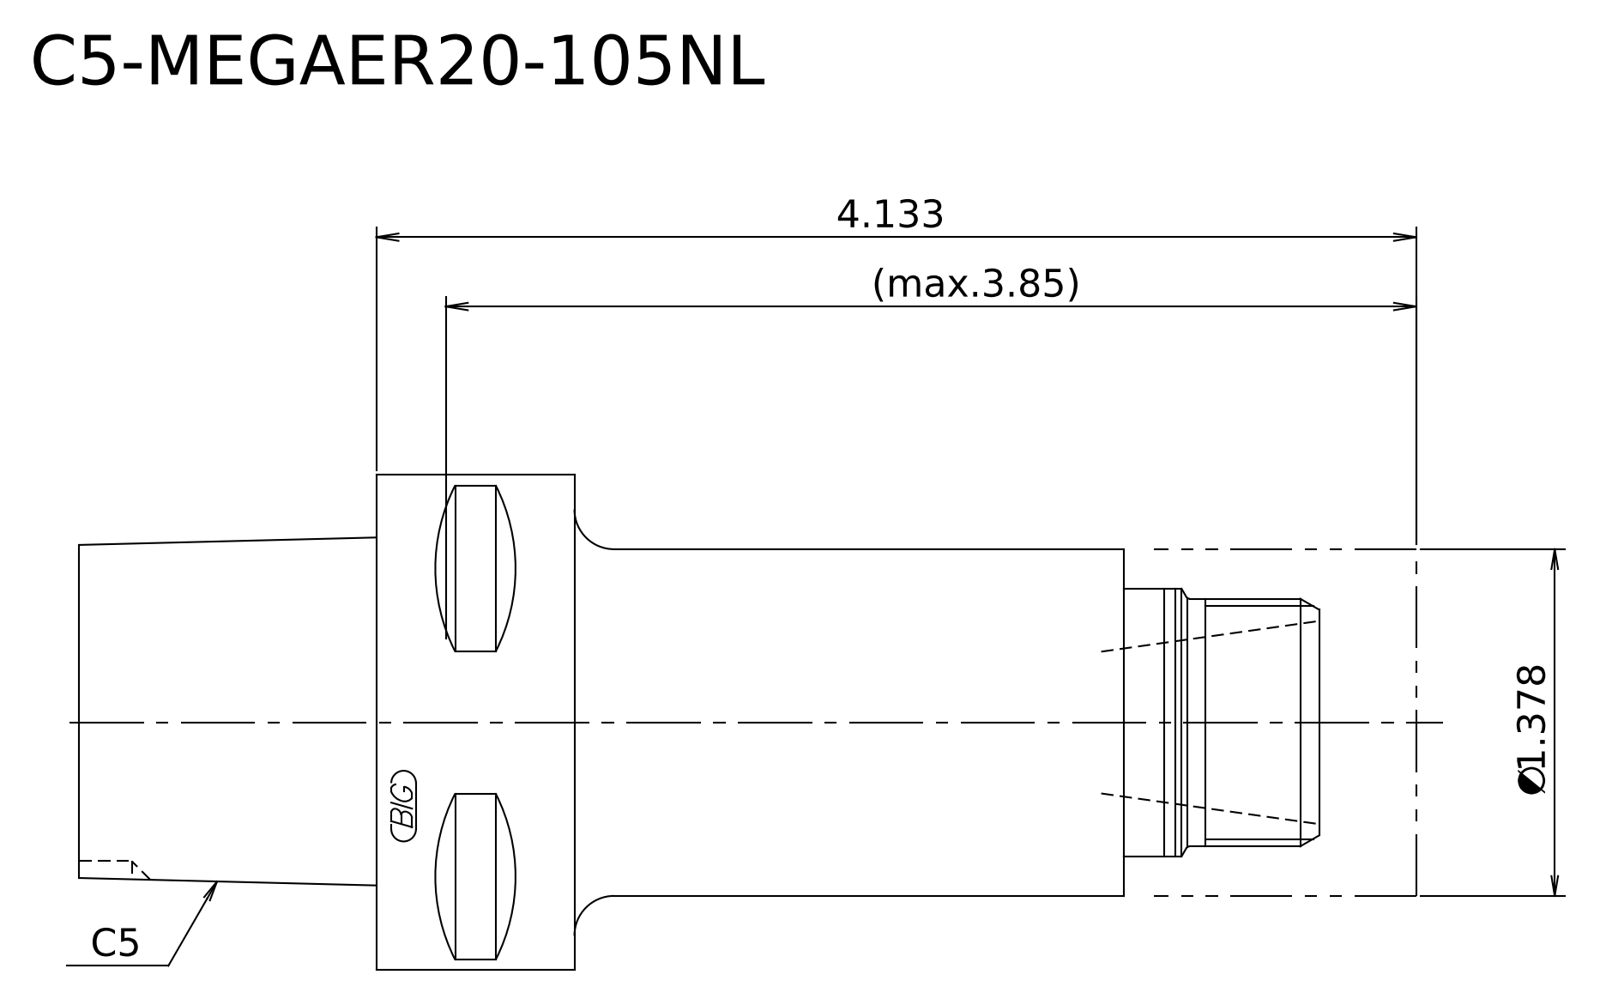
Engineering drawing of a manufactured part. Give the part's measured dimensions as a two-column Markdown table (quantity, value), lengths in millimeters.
| quantity | value |
| --- | --- |
| STEP written by | Kubotek KeyCreator 2011 V10.0.2 (22737) (automotive_design) |
| units | millimeters |
| bodies | 2 solids, 16 faces (7 planar, 5 cylindrical, 4 other) |
| overall size | 135 × 50 × 50 |
| volume | 156 400 mm³ |
| surface area | 22 418 mm² |
| round bosses / shafts (diameter × count) | 50 × 1, 35 × 1, 27 × 1, 25 × 1 |
| main face-to-face distances | 78.5, 26.5, 105, 135, 108.5, 30, 85, 58.5, 20, 50 |
